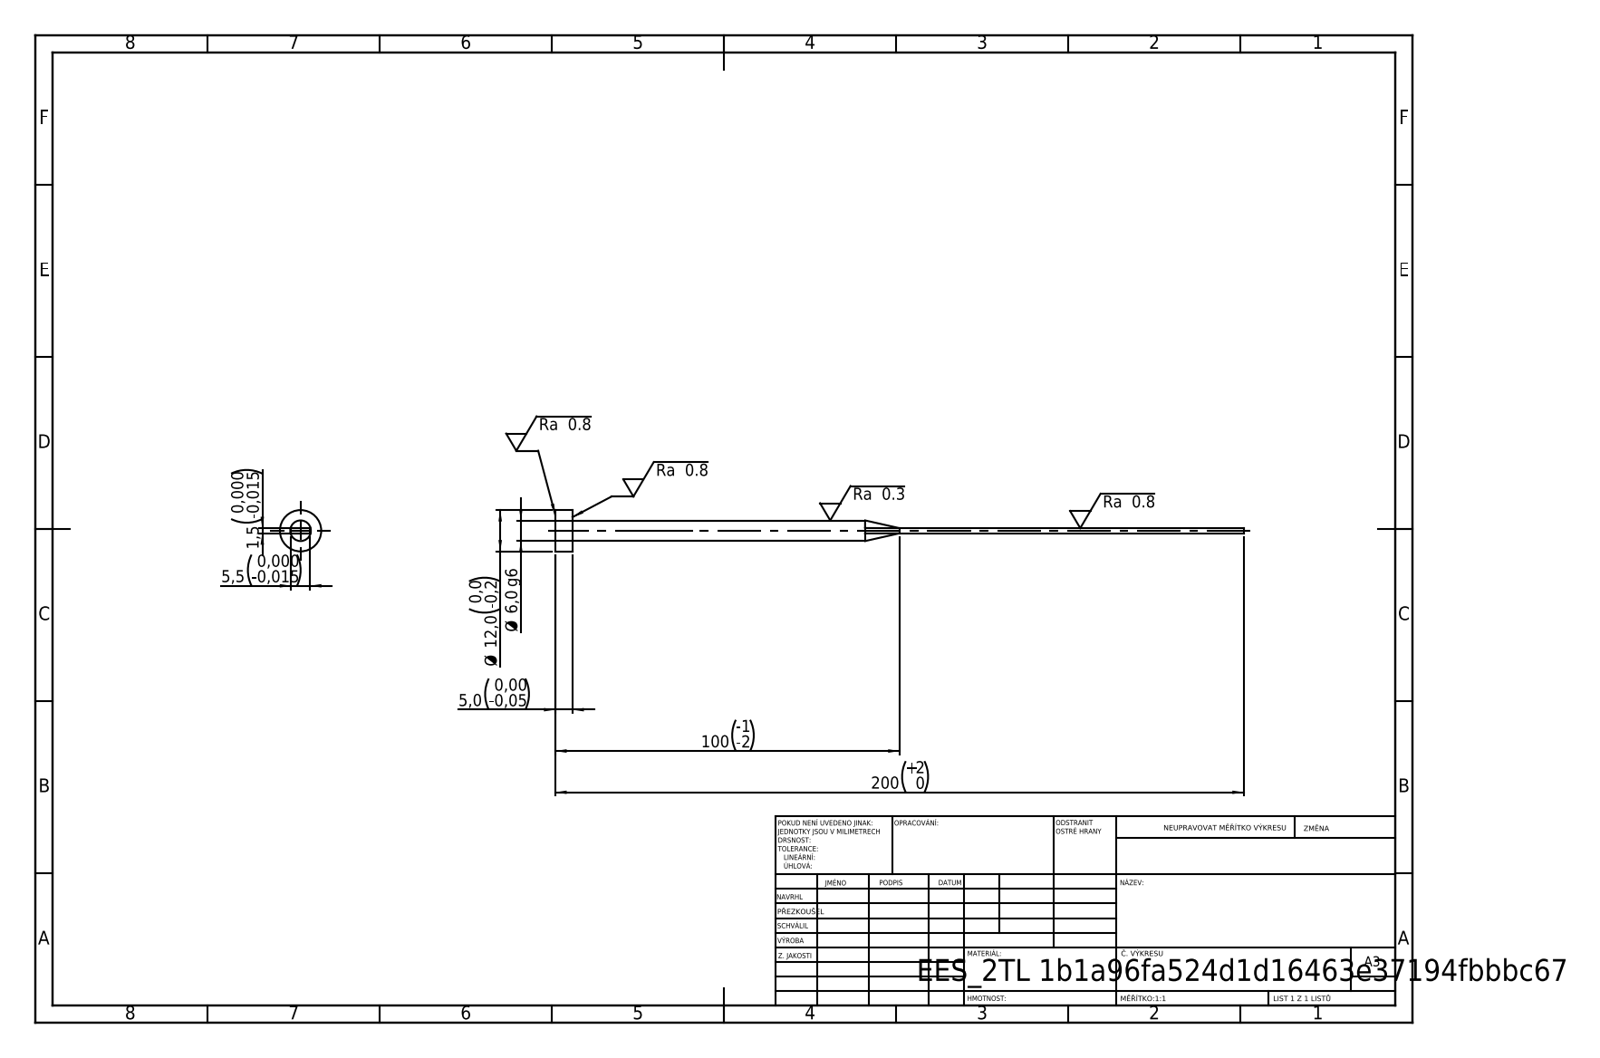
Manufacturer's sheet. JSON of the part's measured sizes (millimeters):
{"step_written_by": "SolidWorks 2019 (CONFIG_CONTROL_DESIGN)", "units": "millimeters", "bodies": {"solids": 1, "faces": 15, "planar": 7, "cylindrical": 4, "other": 4}, "overall_size": [200, 12, 12], "volume_mm3": 3969, "surface_area_mm2": 3556, "round_bosses_or_shafts": [[12, 1], [6, 1]], "face_to_face_distances": [1.5, 5.5, 5, 200, 195]}
